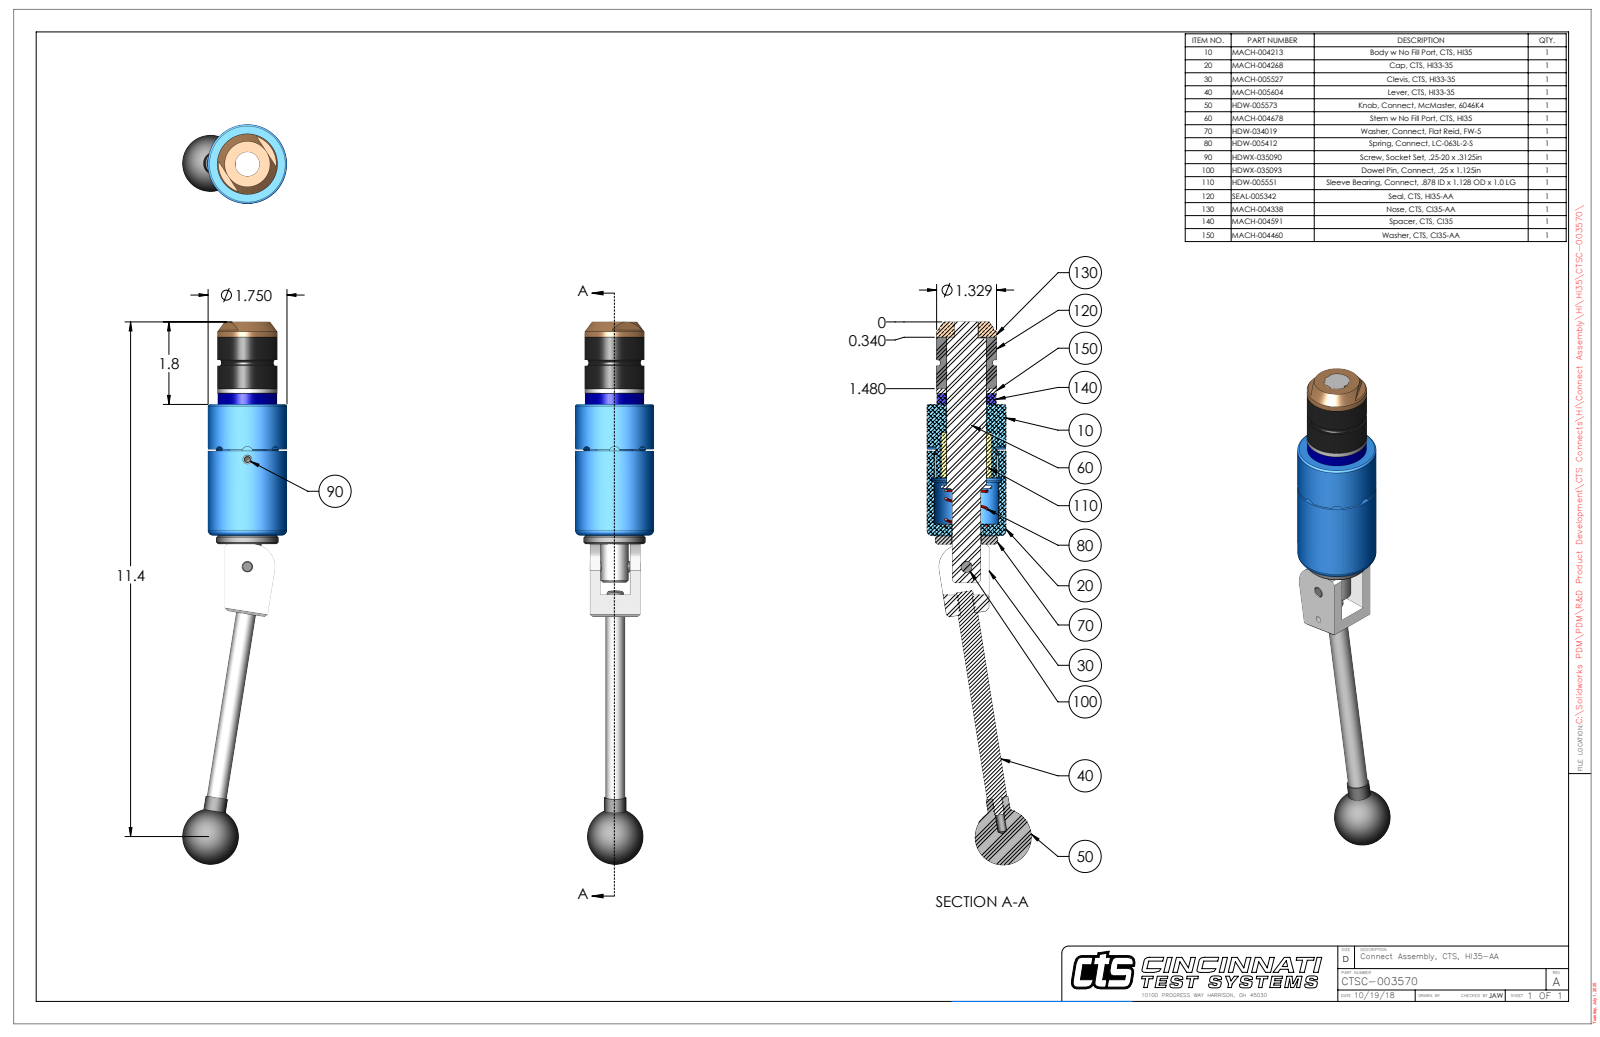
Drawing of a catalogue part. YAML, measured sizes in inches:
part_name: "CTSC-003570"
step_written_by: "SolidWorks 2023 (AUTOMOTIVE_DESIGN)"
units: inches
bodies: {solids: 10, faces: 259, planar: 94, cylindrical: 104, other: 61}
overall_size: [12.039, 2.312, 1.75]
volume: 12.59
surface_area: 77.51
round_holes:
  - {diameter: 0.201, count: 2}
  - {diameter: 0.15, count: 1}
  - {diameter: 0.249, count: 1}
  - {diameter: 0.251, count: 1}
  - {diameter: 0.313, count: 1}
  - {diameter: 0.531, count: 1}
  - {diameter: 0.635, count: 1}
  - {diameter: 0.656, count: 1}
  - {diameter: 0.875, count: 1}
  - {diameter: 0.876, count: 1}
  - {diameter: 0.885, count: 1}
  - {diameter: 1.419, count: 1}
round_bosses_or_shafts:
  - {diameter: 0.25, count: 2}
  - {diameter: 1.75, count: 1}
  - {diameter: 1.38, count: 1}
  - {diameter: 1.329, count: 1}
  - {diameter: 1.312, count: 1}
  - {diameter: 0.871, count: 1}
  - {diameter: 0.869, count: 1}
  - {diameter: 0.625, count: 1}
partial_cylinders:
  - {radius: 0.125, count: 4}
  - {radius: 0.029, count: 2}
  - {radius: 0.5, count: 1}
  - {radius: 0.695, count: 1}
  - {radius: 0.819, count: 1}
face_to_face_distances: [2.912, 1.49, 4.402, 1.14, 0.35, 3.262, 1.25, 0.11, 0.24, 3.152]
hole_center_spacings: [0.74, 2.376, 3.116]
